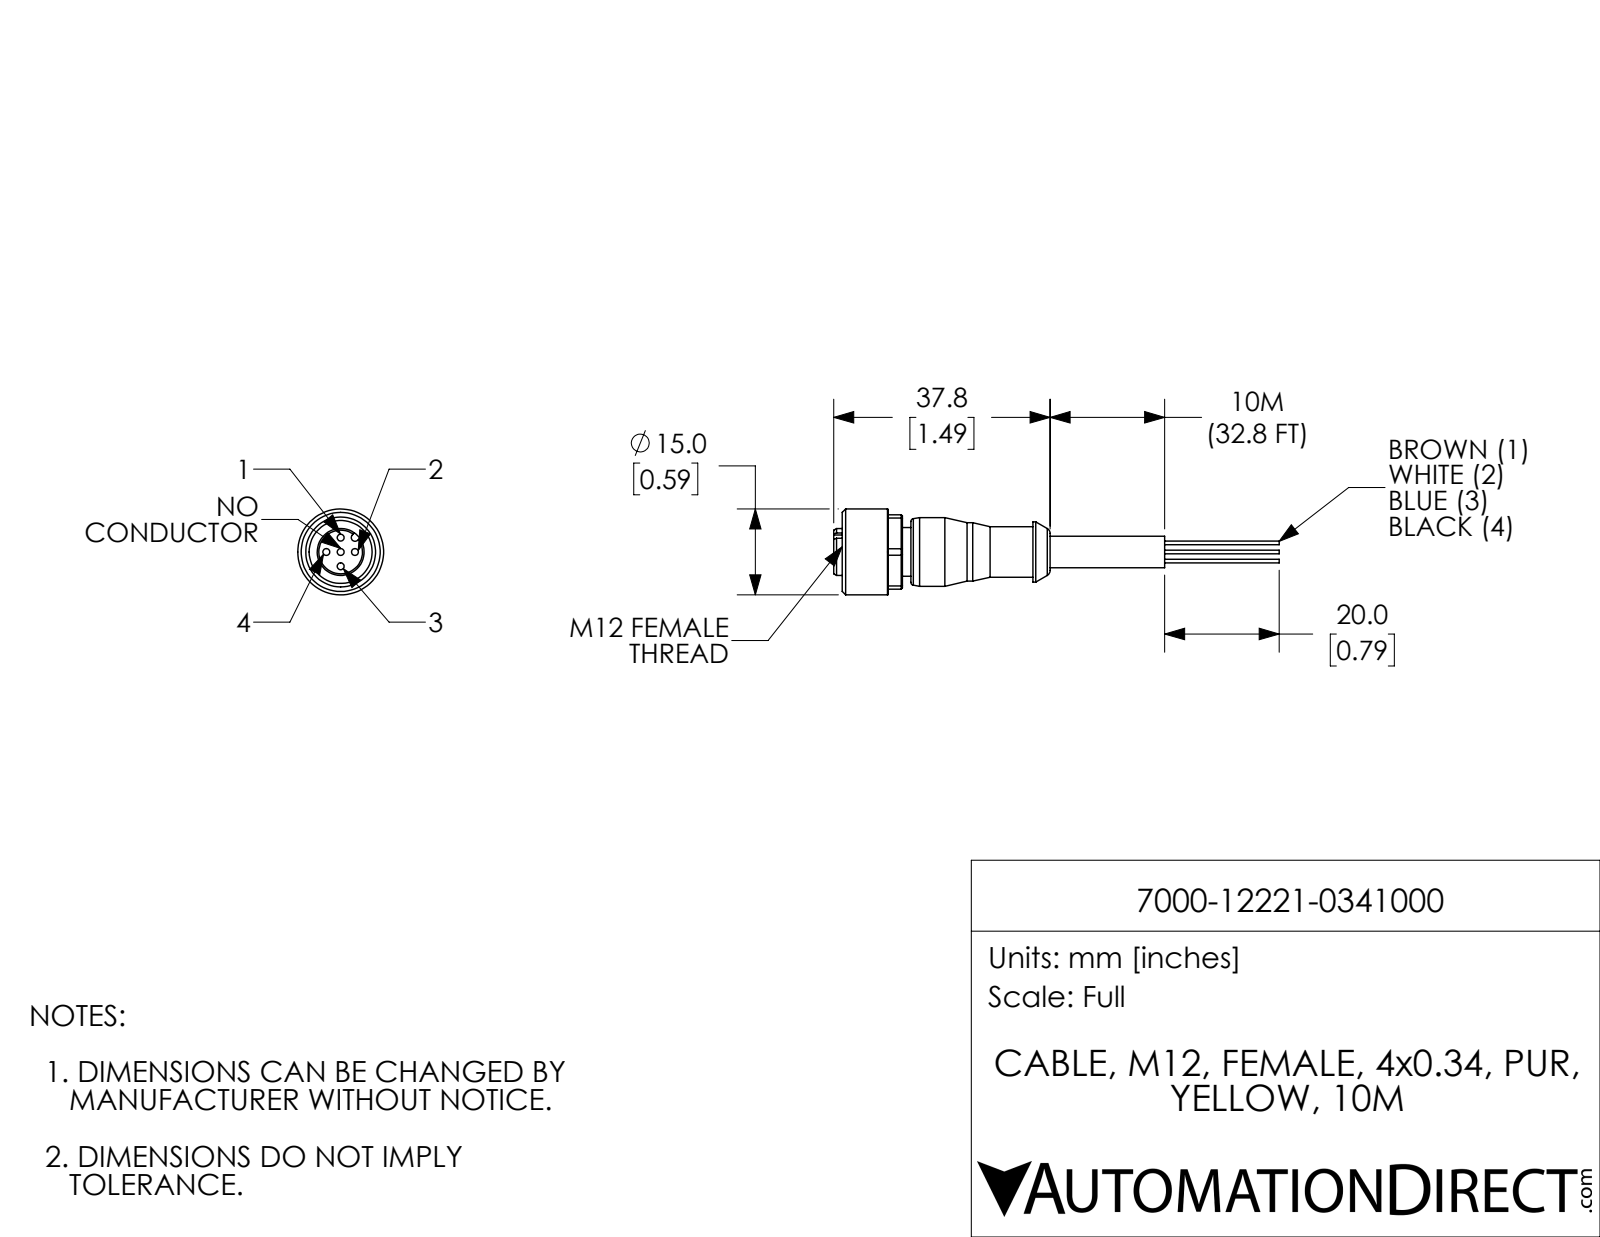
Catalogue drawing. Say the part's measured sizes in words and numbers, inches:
The part is named "7000-12221-0341000". Its 3-D file was written by "SolidWorks 2021 (CONFIG_CONTROL_DESIGN)". It is 1 solid with 103 faces: 33 planar, 43 cylindrical and 27 other. Overall it measures 3.063 by 0.591 by 0.591 inches. Its volume is 0.247 cubic inches and its surface area 4.386 square inches. Round holes: 5 of diameter 0.047, 1 of diameter 0.433. Round bosses or shafts: 4 of diameter 0.026, 1 of diameter 0.591, 1 of diameter 0.472, 1 of diameter 0.413, 1 of diameter 0.402, 1 of diameter 0.346, 1 of diameter 0.335, 1 of diameter 0.323. Partial cylindrical surfaces (rounded edges, fillets, slot ends): 1 of radius 0.026, 1 of radius 0.283. The main face-to-face distances are 0.472, 0.059, 0.118, 0.512, 0.354, 1.016, 0.295, 0.413, 0.098, 0.531. The hole center spacings are 0.098, 0.139, 0.197.
